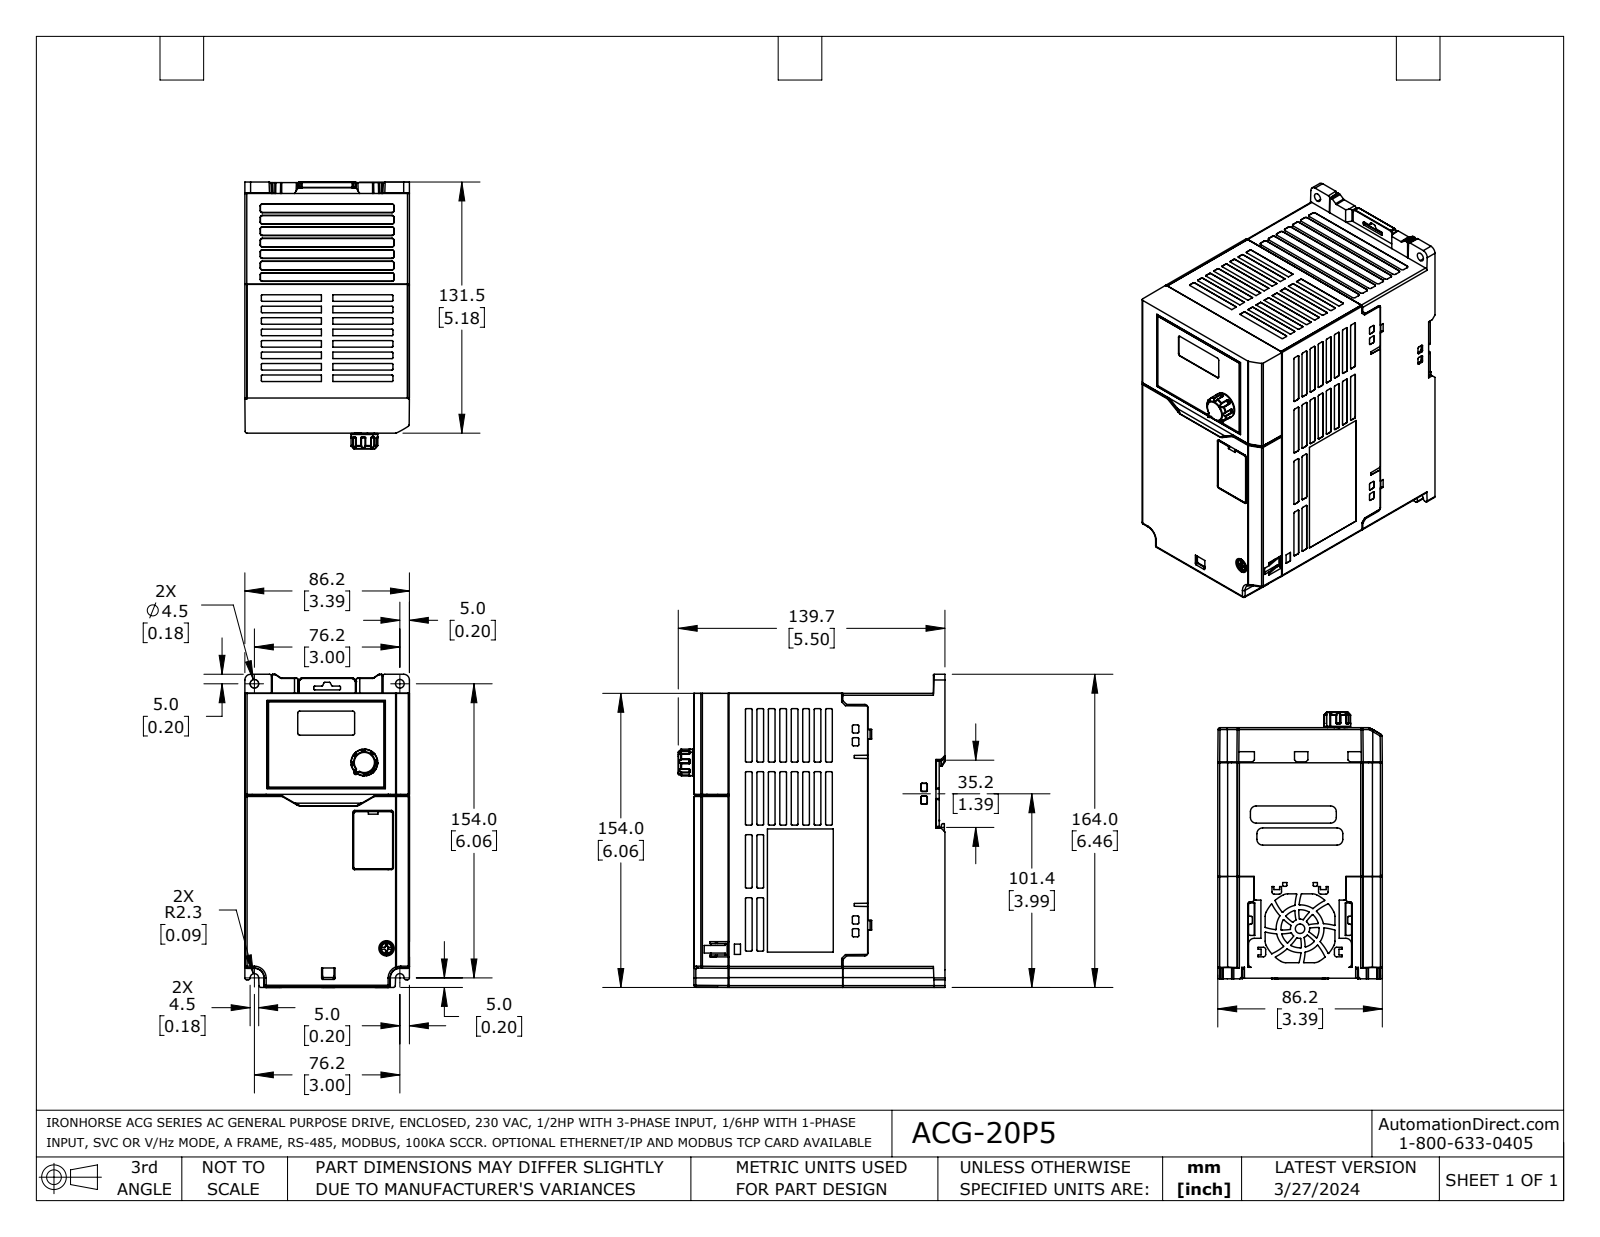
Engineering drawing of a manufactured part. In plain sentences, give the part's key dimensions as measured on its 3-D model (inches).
The part is named "ACG-20P5". Its 3-D file was written by "SolidWorks 2021 (AUTOMOTIVE_DESIGN)". It is 6 solids with 4492 faces: 1868 planar, 1308 cylindrical and 1316 other. Overall it measures 6.457 by 5.5 by 3.394 inches. Its volume is 101.9 cubic inches and its surface area 197.5 square inches. Round holes: 1 of diameter 0.039, 1 of diameter 0.276, 1 of diameter 0.472. Round bosses or shafts: 1 of diameter 0.551, 1 of diameter 0.543, 1 of diameter 0.236. Partial cylindrical surfaces (rounded edges, fillets, slot ends): 343 of radius 0.008, 288 of radius 0.02, 85 of radius 0.039, 46 of radius 0.018, 27 of radius 0.012, 17 of radius 0.031, 16 of radius 0.023, 12 of radius 0.118. The main face-to-face distances are 3.394, 5.059, 3.392, 5.047, 6.063, 6.061, 5.165, 0.106, 3.39, 6.061. The hole center spacings are 0.276, 3.675, 3.858.
